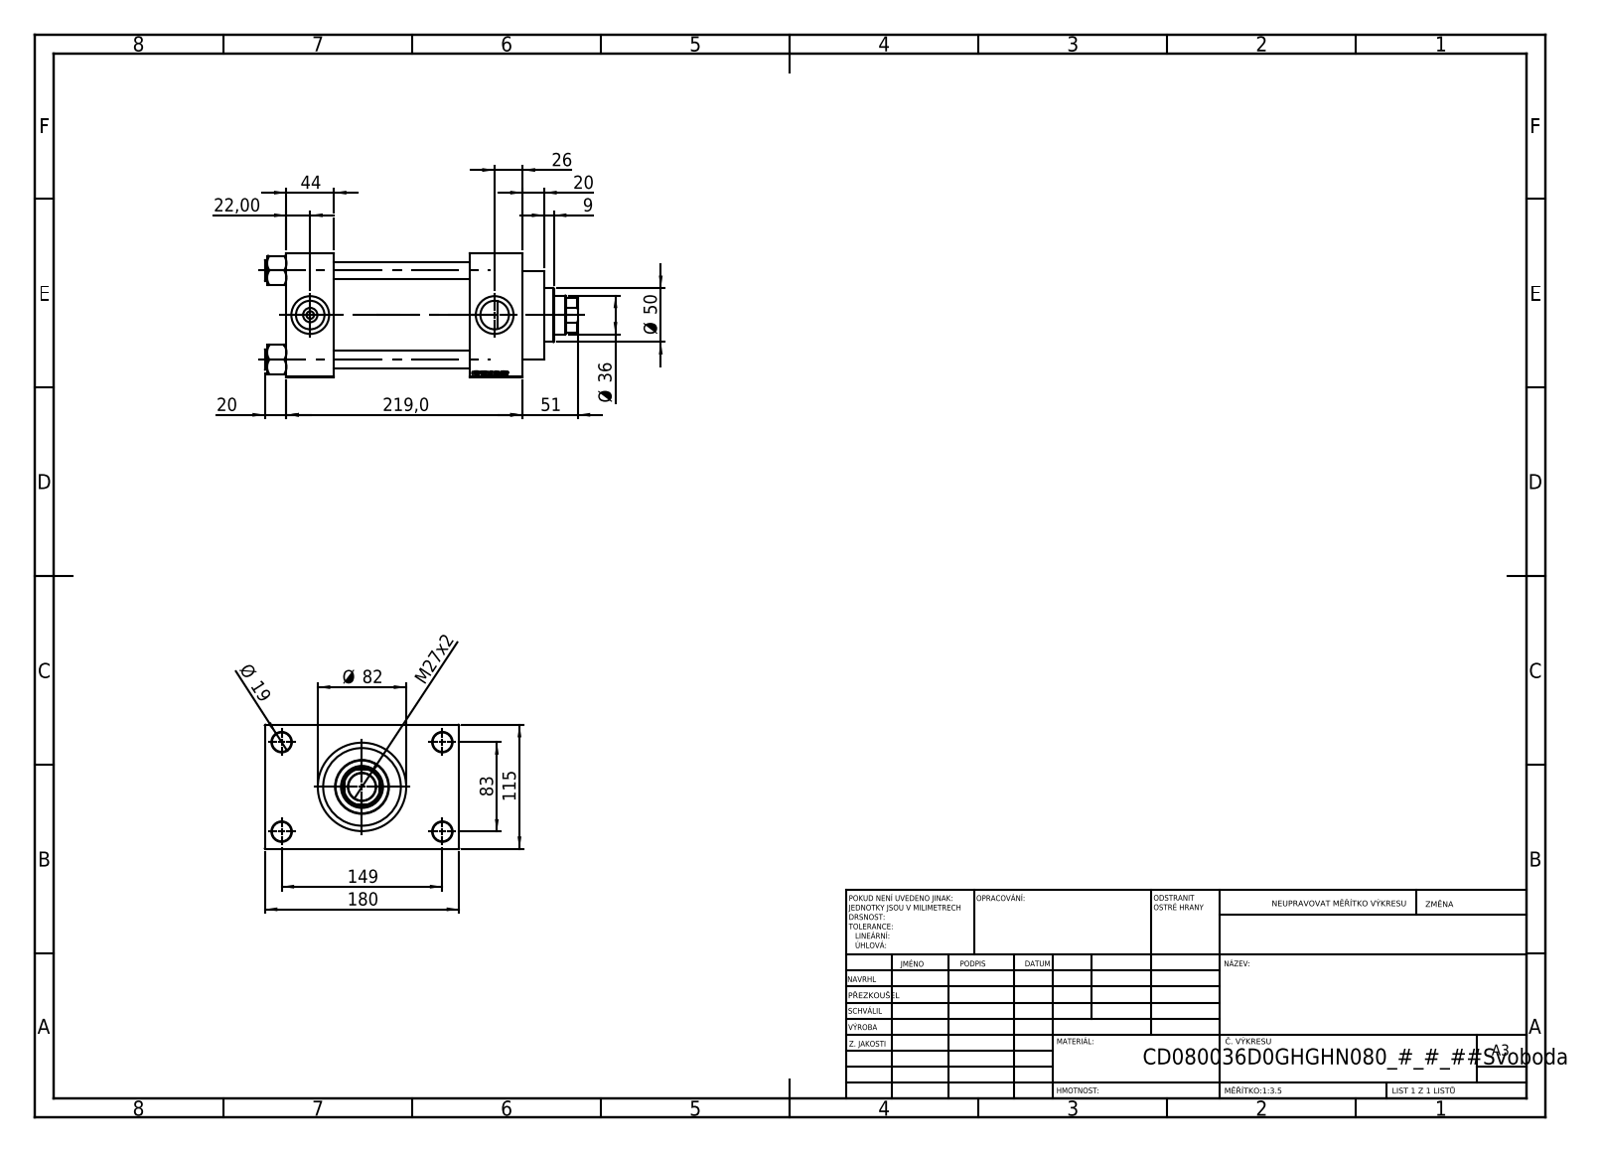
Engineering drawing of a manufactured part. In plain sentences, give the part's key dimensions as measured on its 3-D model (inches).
The part is named "V215CD_VC_A; V215CD_D_Body; V215CD_NUT_M5_D; V215CD_D_TYCINKA (+1 more)". Its 3-D file was written by "SolidWorks 2019 (CONFIG_CONTROL_DESIGN)". It is 11 solids with 1151 faces: 545 planar, 88 cylindrical and 518 other. Overall it measures 11.417 by 7.087 by 4.528 inches. Its volume is 130.3 cubic inches and its surface area 537.4 square inches. Round holes: 4 of diameter 0.63, 4 of diameter 0.709, 2 of diameter 0.276, 2 of diameter 1.041, 2 of diameter 1.378, 1 of diameter 1.004, 1 of diameter 1.417, 1 of diameter 1.535, 1 of diameter 2.402, 1 of diameter 2.835, 1 of diameter 3.15. Round bosses or shafts: 4 of diameter 0.748, 1 of diameter 3.386, 1 of diameter 3.228, 1 of diameter 1.969. Partial cylindrical surfaces (rounded edges, fillets, slot ends): 1 of radius 0.689. The main face-to-face distances are 4.528, 4.961, 6.89, 1.929, 6.693, 1.732, 8.622, 1.28, 5.807, 7.087. The hole center spacings are 1.305, 2.302, 3.256, 3.357, 3.513, 4.561, 5.607, 3.268.
